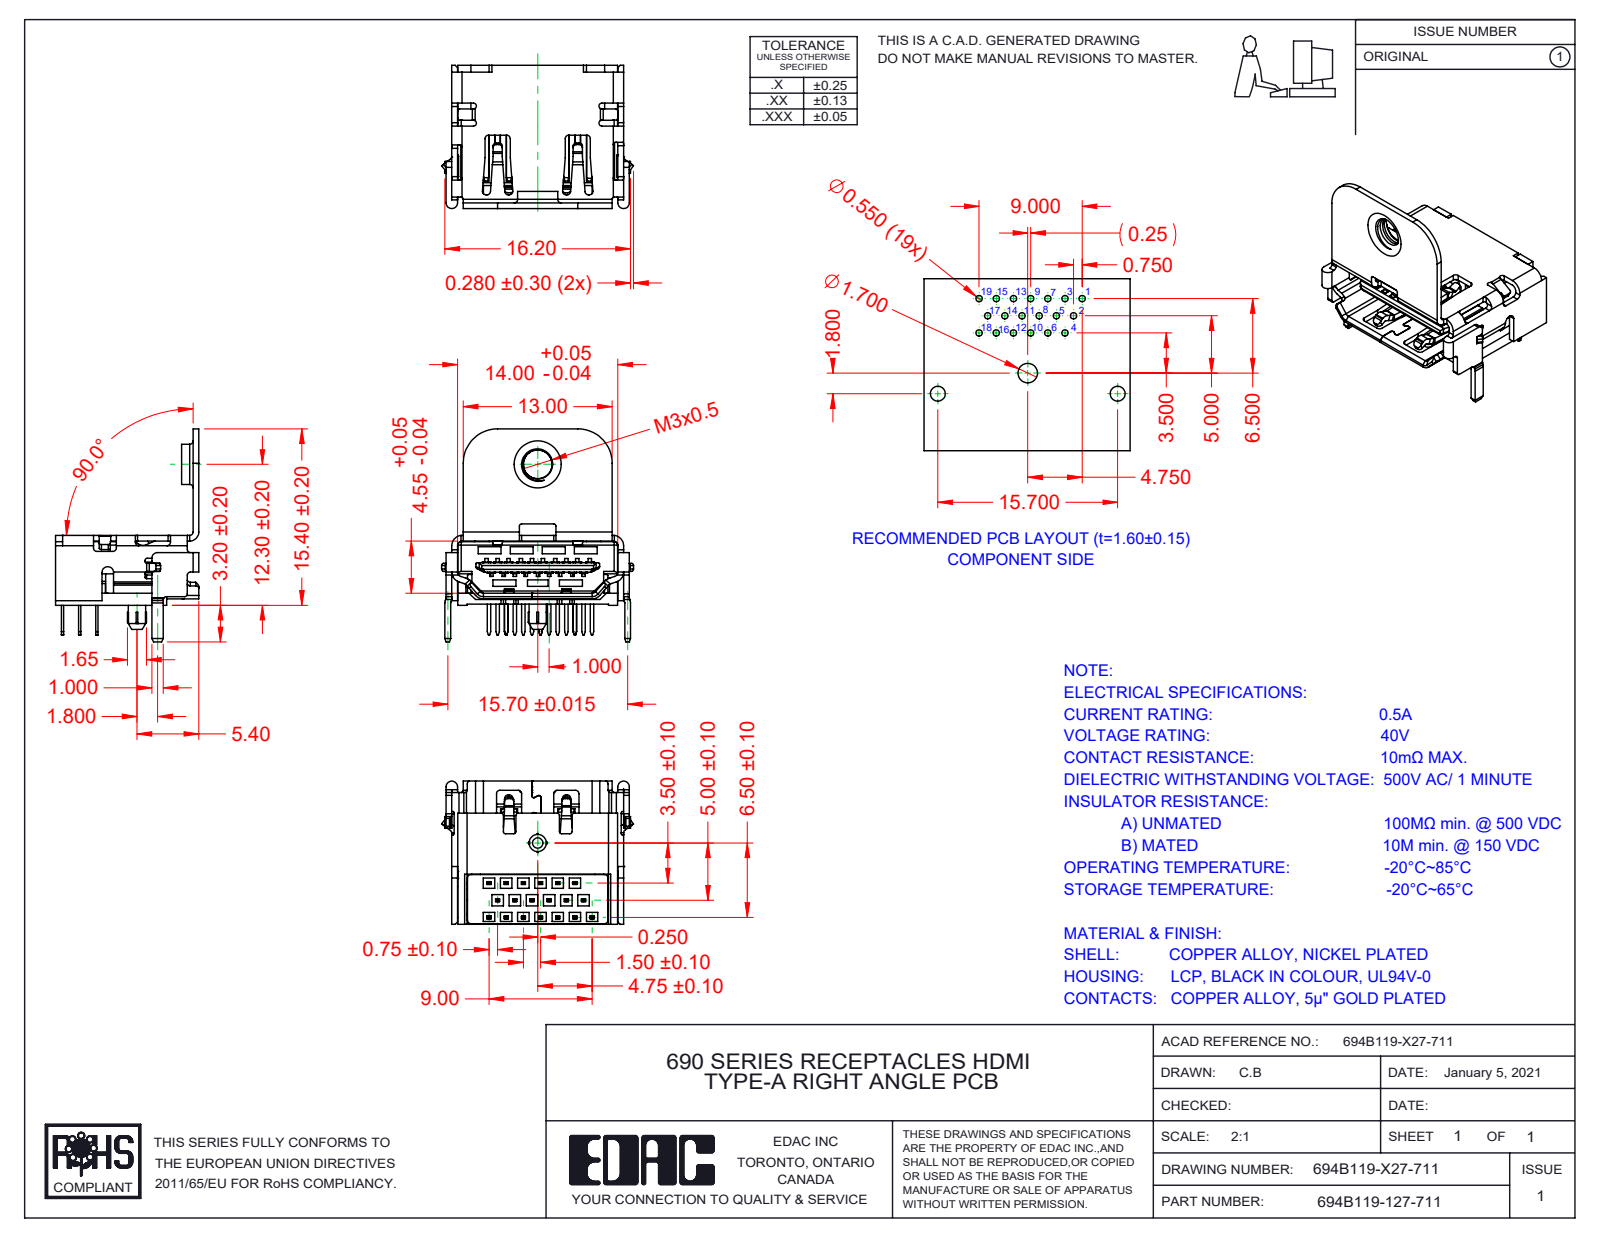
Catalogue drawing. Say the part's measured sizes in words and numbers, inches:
The part is named "Contact 17 694B119-X27-711; Insulator2 694B119-X27-711; Contact 9 694B119-X27-711; Contact 1 694B119-X27-711 (+8 more)". Its 3-D file was written by "SolidWorks 2020 (AUTOMOTIVE_DESIGN)". It is 22 solids with 2042 faces: 1664 planar, 326 cylindrical and 52 other. Overall it measures 0.732 by 0.659 by 0.492 inches. Its volume is 0.037 cubic inches and its surface area 4.025 square inches. Round holes: 1 of diameter 0.098. Round bosses or shafts: 1 of diameter 0.138, 1 of diameter 0.059. Partial cylindrical surfaces (rounded edges, fillets, slot ends): 45 of radius 0.008, 45 of radius 0.012, 44 of radius 0.004, 16 of radius 0.01, 12 of radius 0.02, 8 of radius 0.006, 7 of radius 0.016, 6 of radius 0.035. The main face-to-face distances are 0.02, 0.199, 0.1, 0.02, 0.099, 0.078, 0.022, 0.179, 0.197, 0.12.
